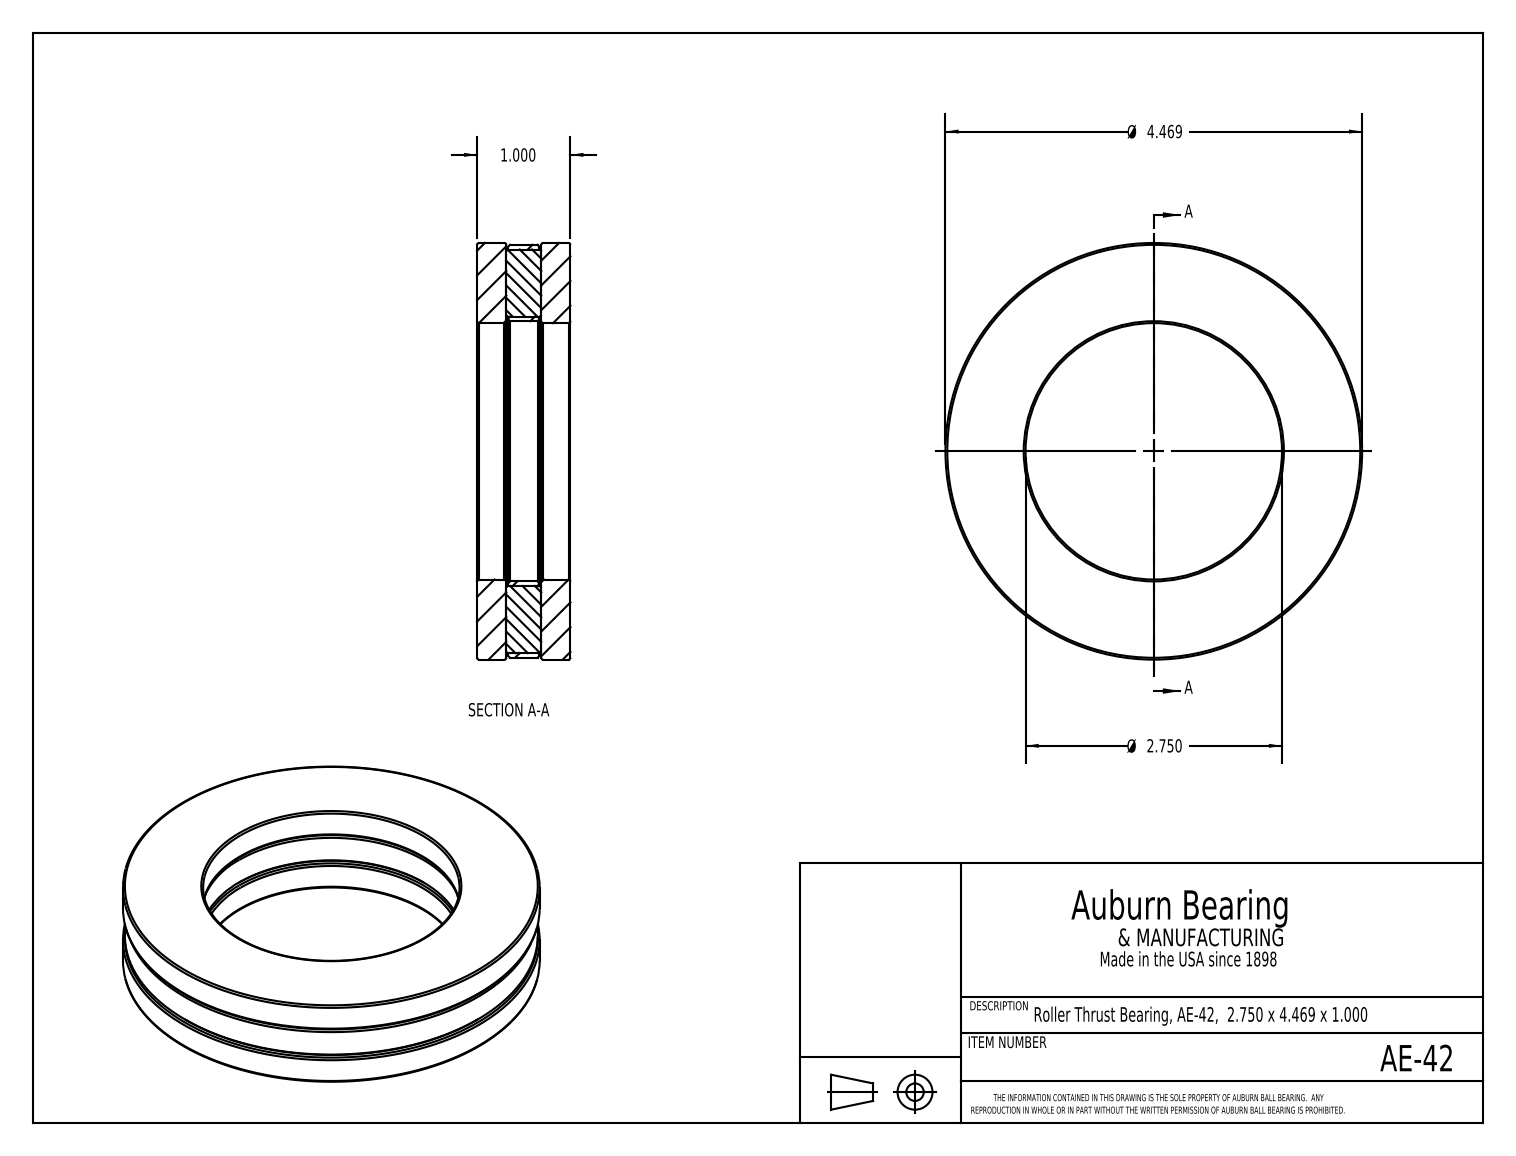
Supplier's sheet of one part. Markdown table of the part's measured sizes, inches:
| quantity | value |
| --- | --- |
| part name | AE-42 |
| STEP written by | SolidWorks 2017 (CONFIG_CONTROL_DESIGN) |
| units | inches |
| bodies | 7 solids, 60 faces (30 planar, 10 cylindrical, 20 other) |
| overall size | 4.469 × 4.469 × 1 |
| volume | 9.142 in³ |
| surface area | 82.99 in² |
| round holes (diameter × count) | 2.75 × 1, 2.79 × 1 |
| round bosses / shafts (diameter × count) | 0.375 × 2, 4.469 × 1, 4.429 × 1 |
| main face-to-face distances | 0.313, 0.687, 0.333, 0.667, 0.02, 0.355, 0.375, 1, 0.335, 1.257 |
